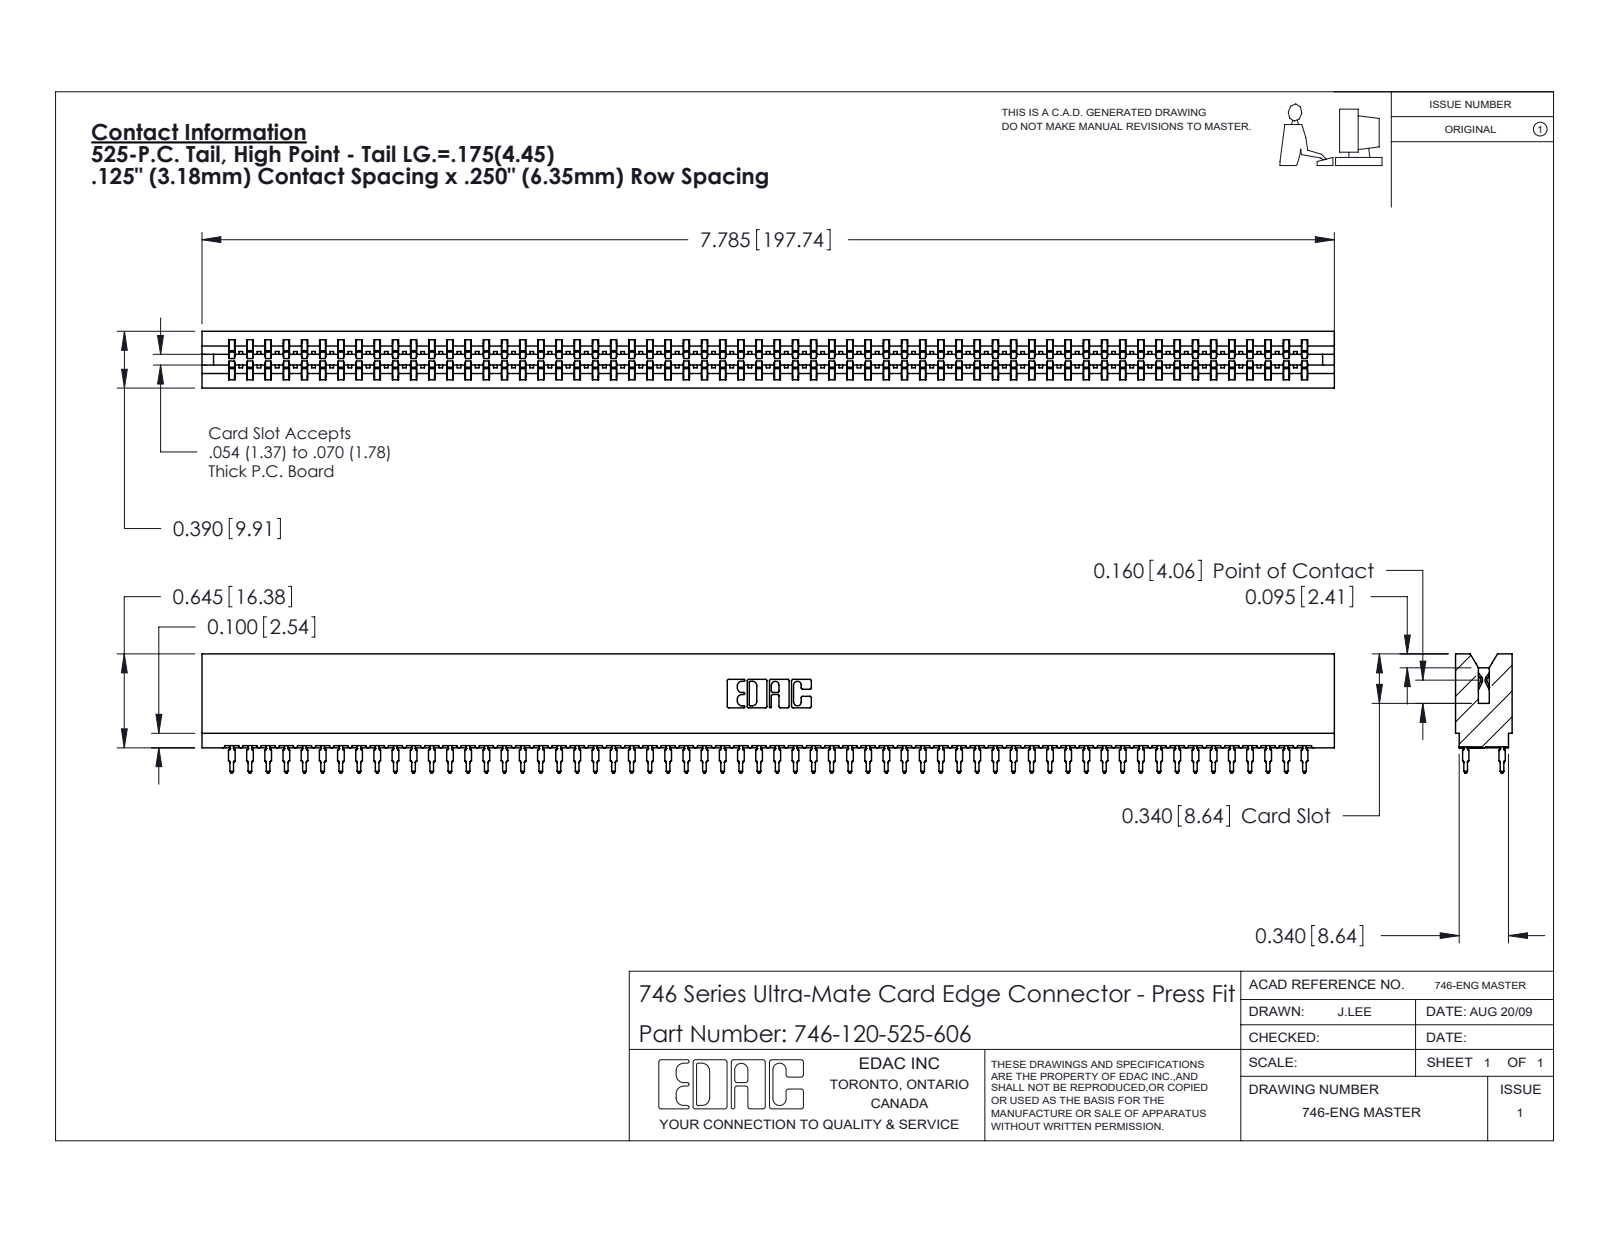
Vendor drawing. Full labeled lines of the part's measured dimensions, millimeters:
Part name (STEP PRODUCT): 746 Part_.340 Slot Depth - 06; 746-292-001_525; 746-120-525-606
STEP written by: SolidWorks 2020 (CONFIG_CONTROL_DESIGN)
Units: millimetres
Bodies: 121 solids, 10838 faces (5576 planar, 2142 cylindrical, 3120 other)
Overall size (bounding box): 197.7 × 20.8 × 9.9
Volume: 22 550 mm³ · Surface area: 33 090 mm²
Partial cylindrical surfaces — rounded edges, fillets, slot ends (radius × count): R0.5 ×240, R0.4 ×61, R0.3 ×22, R0.1 ×8, R0.3 ×8, R0.2 ×6, R0.8 ×6, R0.7 ×3
Main face-to-face distances: 1.4, 8.5, 9.9, 0.6, 6.4, 7.8, 7, 2.1, 0.4, 1.5
